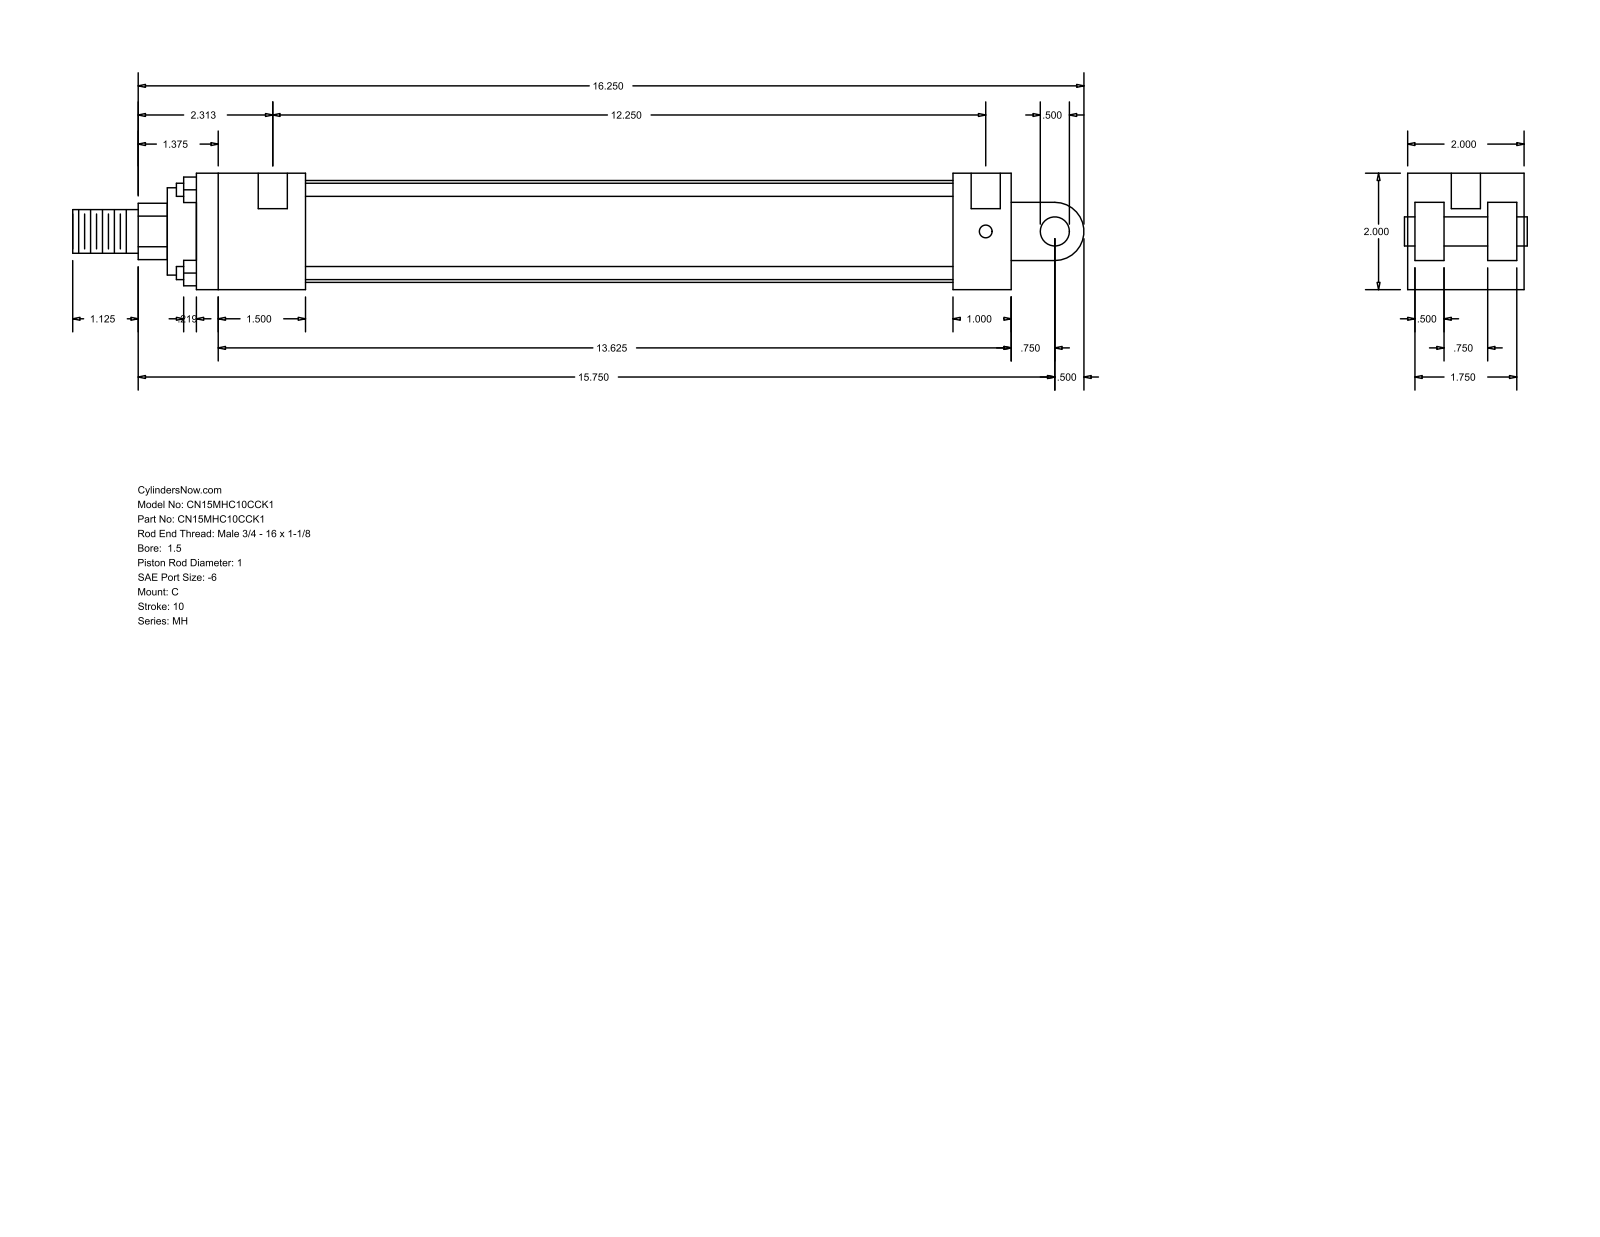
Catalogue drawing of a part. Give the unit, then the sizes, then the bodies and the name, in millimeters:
Units: millimetres
Overall size (bounding box): 441.32 × 50.8 × 50.8
Round holes (diameter × count): ⌀5.56 ×4, ⌀12.7 ×2
Round bosses / shafts (diameter × count): ⌀5.71 ×4, ⌀44.45 ×1, ⌀38.1 ×1, ⌀25.4 ×1, ⌀19.05 ×1, ⌀12.7 ×1
Partial cylindrical surfaces — rounded edges, fillets, slot ends (radius × count): R12.29 ×1, R12.7 ×1
Main face-to-face distances: 50.8, 12.7, 47.63, 25.4, 3.17, 15.87, 34.93, 31.76, 355.6, 38.1
Hole centre spacings: 314.33, 3.18, 311.15
Bodies: 0 solids, 99 faces (70 planar, 29 cylindrical, 0 other)
Part name (STEP PRODUCT): MH_C__0150_1
STEP written by: GSSL Pune (CONFIG_CONTROL_DESIGN)
